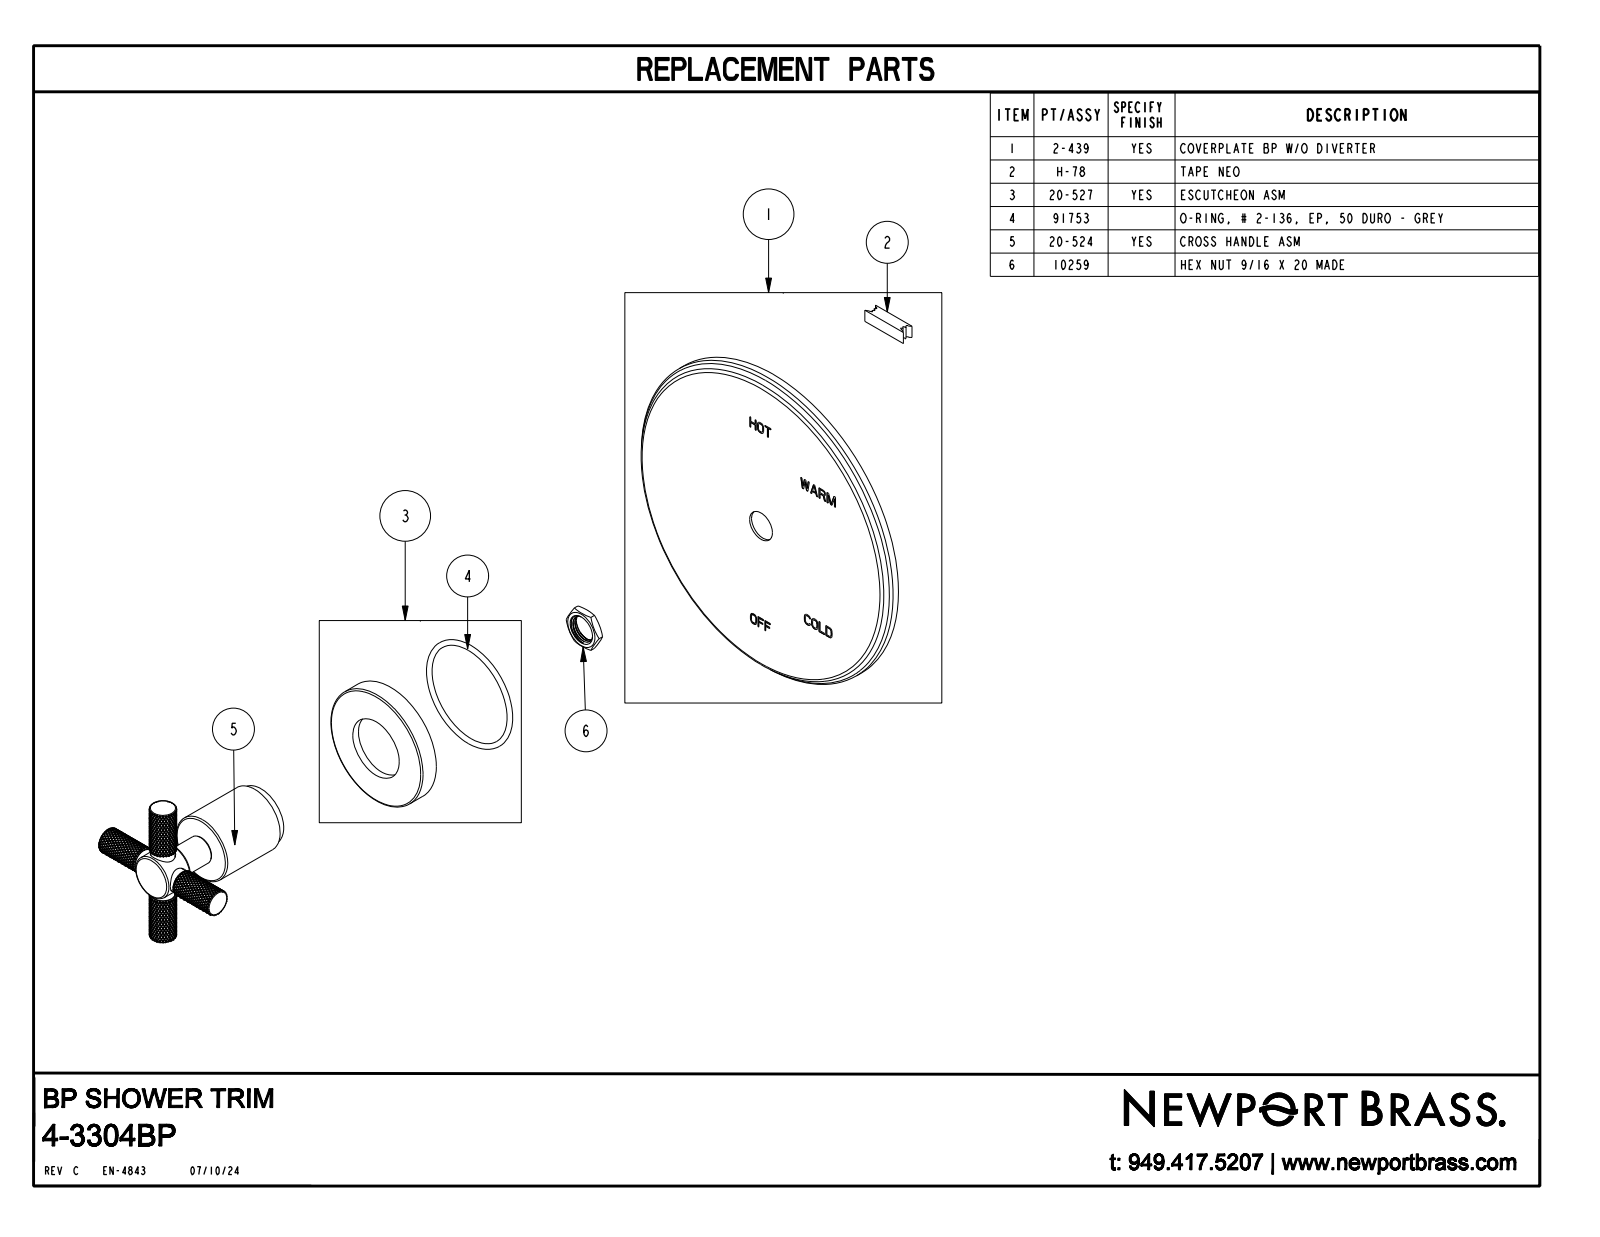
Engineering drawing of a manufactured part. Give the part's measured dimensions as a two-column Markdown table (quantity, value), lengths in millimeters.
| quantity | value |
| --- | --- |
| part name | 4-3304BP |
| STEP written by | CREO PARAMETRIC BY PTC INC, 2018400 (CONFIG_CONTROL_DESIGN) |
| units | millimeters |
| bodies | 1 solid, 11497 faces (347 planar, 2158 cylindrical, 8992 other) |
| overall size | 165.1 × 165.1 × 85.8 |
| volume | 245 300 mm³ |
| surface area | 59 810 mm² |
| round holes (diameter × count) | 11.8 × 2 |
| round bosses / shafts (diameter × count) | 12.7 × 2, 11.2 × 2, 165.1 × 1, 60.3 × 1, 33.4 × 1, 31.8 × 1, 21.6 × 1, 14.3 × 1 |
| main face-to-face distances | 8, 17.5, 9.5, 53, 45.1, 35.6, 85.8, 77.9, 68.4, 32.8 |
